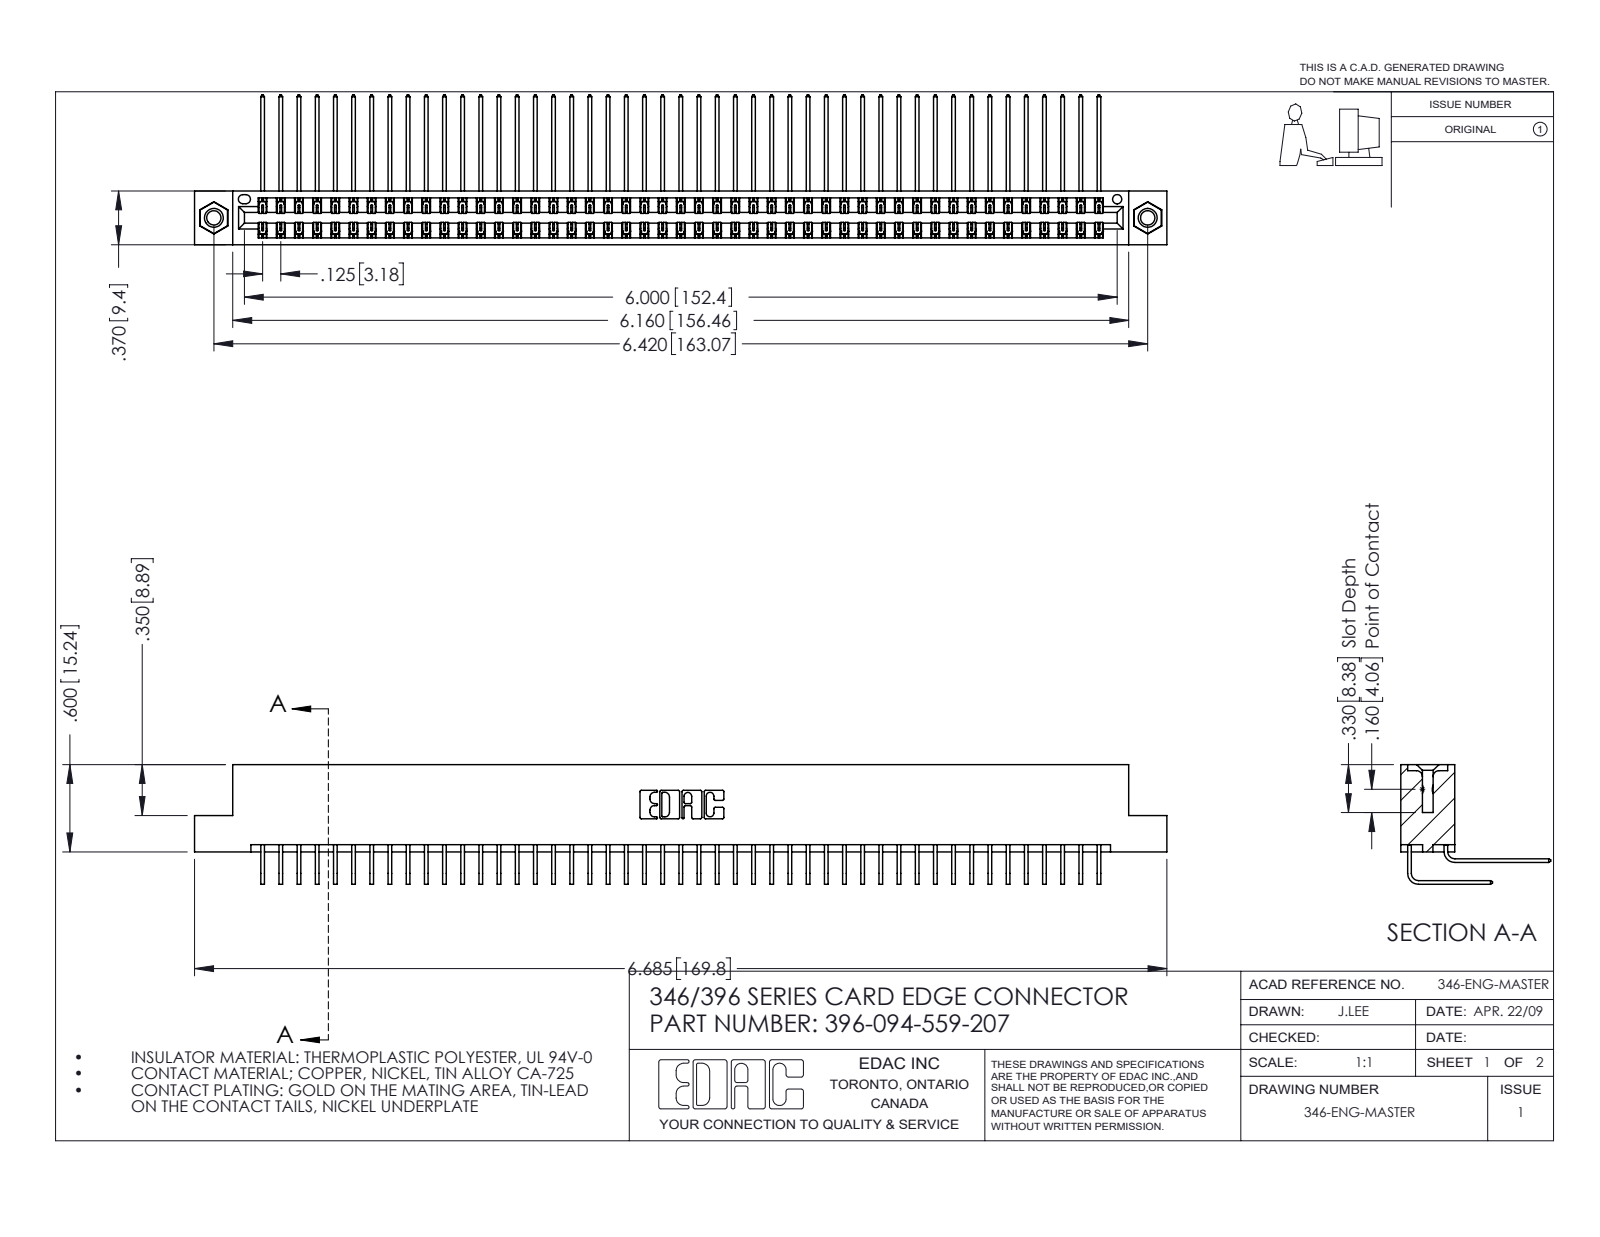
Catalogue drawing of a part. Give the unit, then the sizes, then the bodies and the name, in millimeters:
Units: millimetres
Overall size (bounding box): 169.8 × 26.2 × 20.9
Round holes (diameter × count): ⌀2.5 ×2, ⌀3.2 ×2, ⌀4 ×2, ⌀1.6 ×1
Round bosses / shafts (diameter × count): ⌀3.9 ×2
Partial cylindrical surfaces — rounded edges, fillets, slot ends (radius × count): R0.2 ×141, R0.3 ×22, R0.2 ×6, R0.8 ×6, R0.7 ×3, R0.4 ×2, R0.6 ×2, R0.6 ×2
Main face-to-face distances: 1.2, 8.2, 0.6, 9.4, 6.4, 1.8, 7.6, 7, 3.8, 5.6
Hole centre spacings: 6.2, 157.8, 163.1
Volume: 17 120 mm³ · Surface area: 26 250 mm²
Bodies: 97 solids, 5258 faces (3586 planar, 1656 cylindrical, 16 other)
Part name (STEP PRODUCT): 345-250-001_345-250-005-103; 345-292-001_559 Tail - 2; 396-094-559-207; 345-292-001_558 559 Tail - 1 (+1 more)
STEP written by: SolidWorks 2016 (CONFIG_CONTROL_DESIGN)
